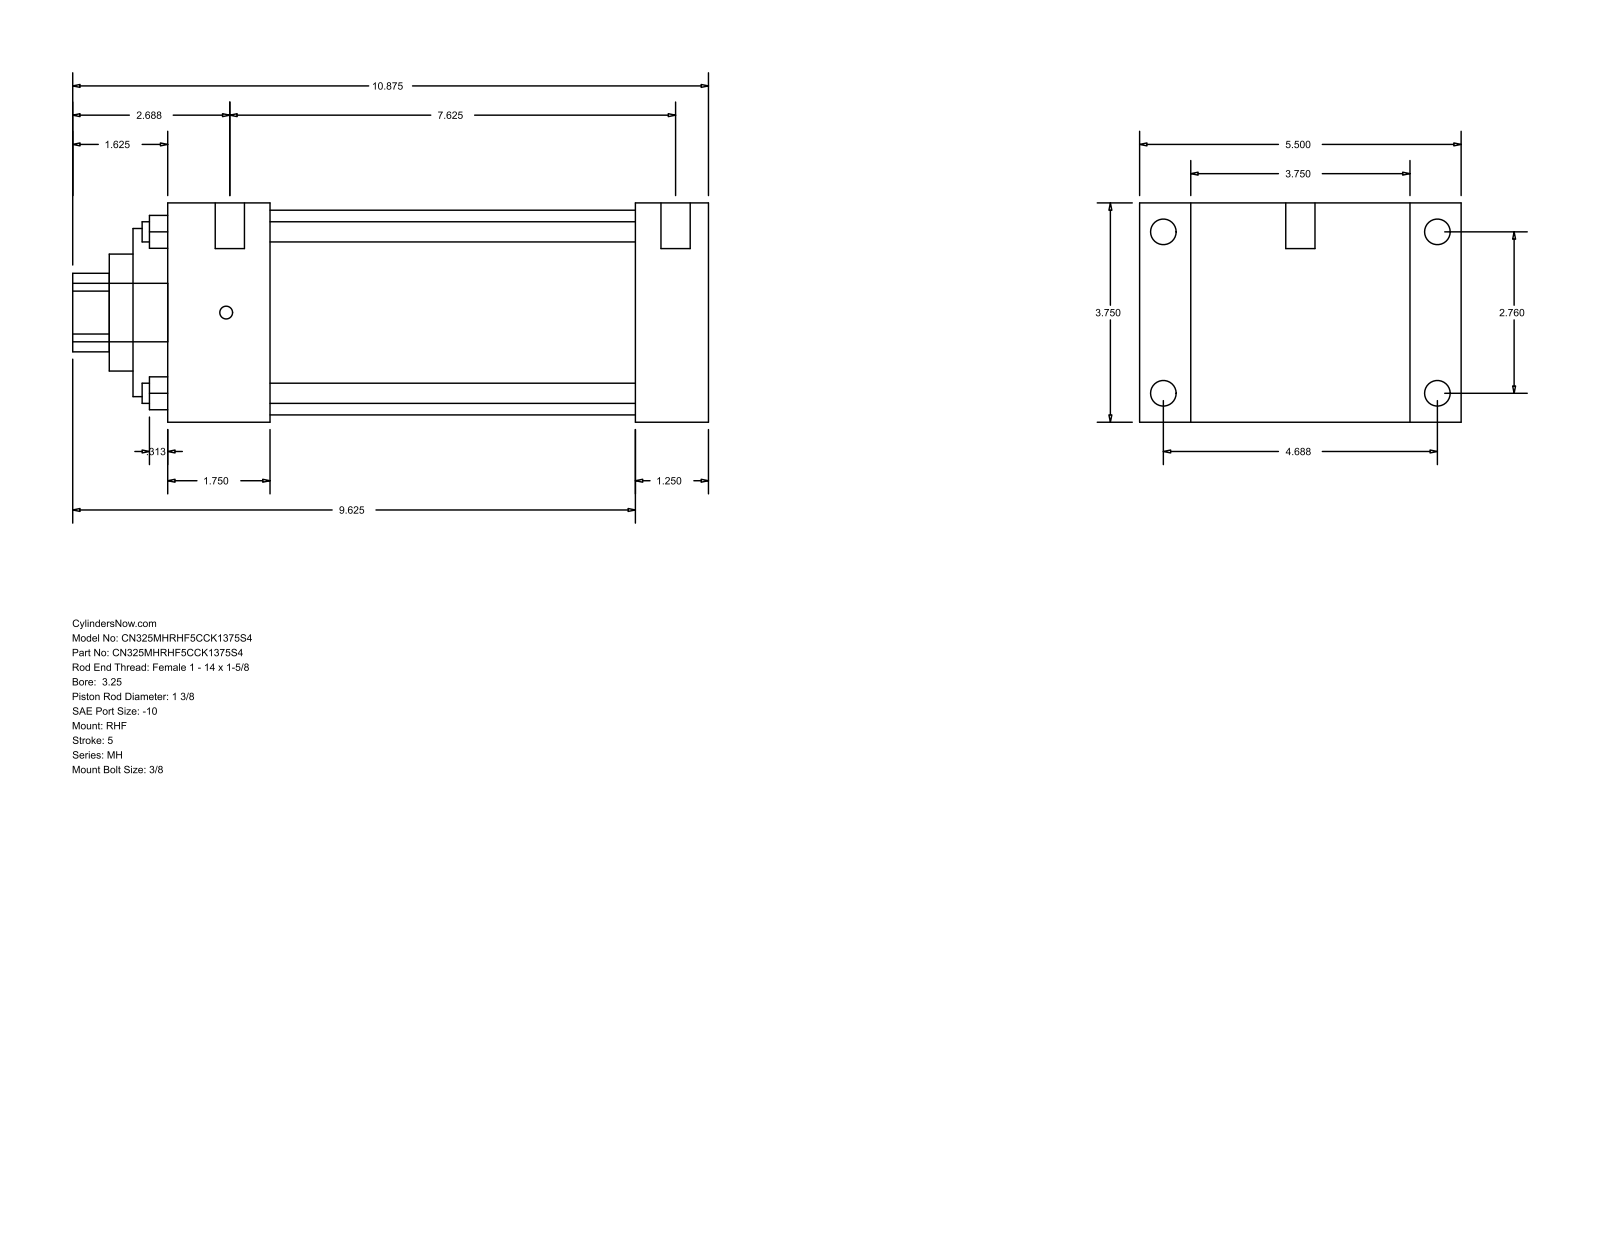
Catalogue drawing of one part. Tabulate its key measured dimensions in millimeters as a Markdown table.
| quantity | value |
| --- | --- |
| part name | MH_RHF__0325_1.375 |
| STEP written by | GSSL Pune (CONFIG_CONTROL_DESIGN) |
| units | millimeters |
| bodies | 0 solids, 90 faces (61 planar, 29 cylindrical, 0 other) |
| overall size | 276.23 × 139.7 × 95.25 |
| round holes (diameter × count) | 8.76 × 4, 34.92 × 1, 50.8 × 1, 73.03 × 1, 88.9 × 1 |
| round bosses / shafts (diameter × count) | 11.13 × 4, 5.56 × 4, 12.7 × 2, 25.4 × 1 |
| partial cylindrical surfaces (radius × count) | 17.06 × 1 |
| main face-to-face distances | 95.24, 31.76, 22.23, 117.47, 203.2, 234.96, 139.7, 44.45, 158.75, 190.51 |
| hole center spacings | 49.57, 70.1, 99.14 |
